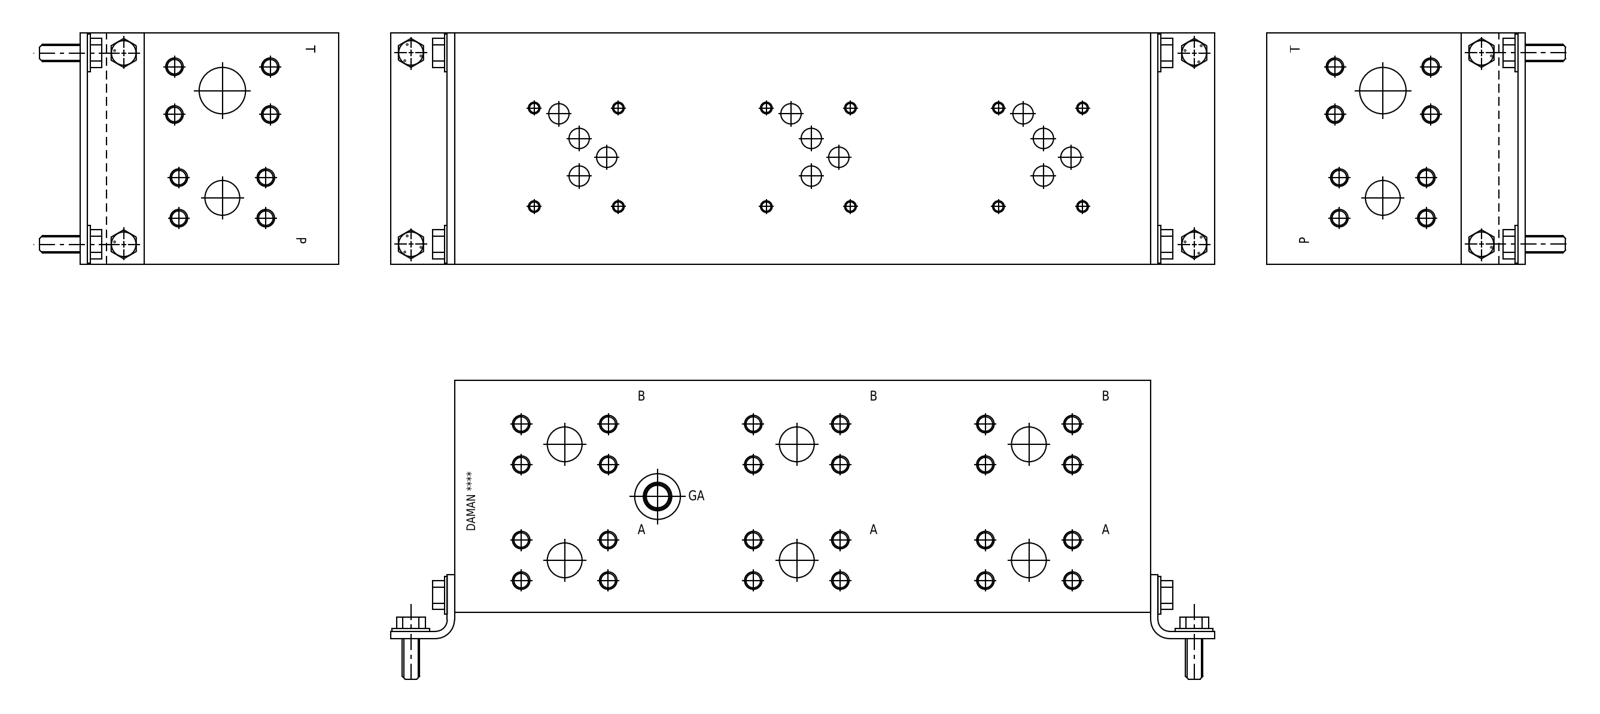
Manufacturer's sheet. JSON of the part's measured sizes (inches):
{"part_name": "D05HP035F", "step_written_by": "Autodesk Inventor 2021 (AUTOMOTIVE_DESIGN)", "units": "inches", "bodies": {"solids": 1, "faces": 812, "planar": 426, "cylindrical": 139, "other": 247}, "overall_size": [15, 5, 5], "volume_in3": 366.9, "surface_area_in2": 427.1, "round_holes": [[0.312, 34], [0.375, 34], [0.201, 12], [0.25, 12], [0.438, 12], [0.75, 7], [0.484, 1], [0.508, 1], [0.562, 1], [0.572, 1], [0.985, 1], [1, 1]], "face_to_face_distances": [5, 15, 1, 4, 14, 0.031, 0.969, 4.969, 0.998, 0.75], "hole_center_spacings": [5, 5.59, 5.076, 0.874, 1.034, 10, 1.874, 2.067]}
